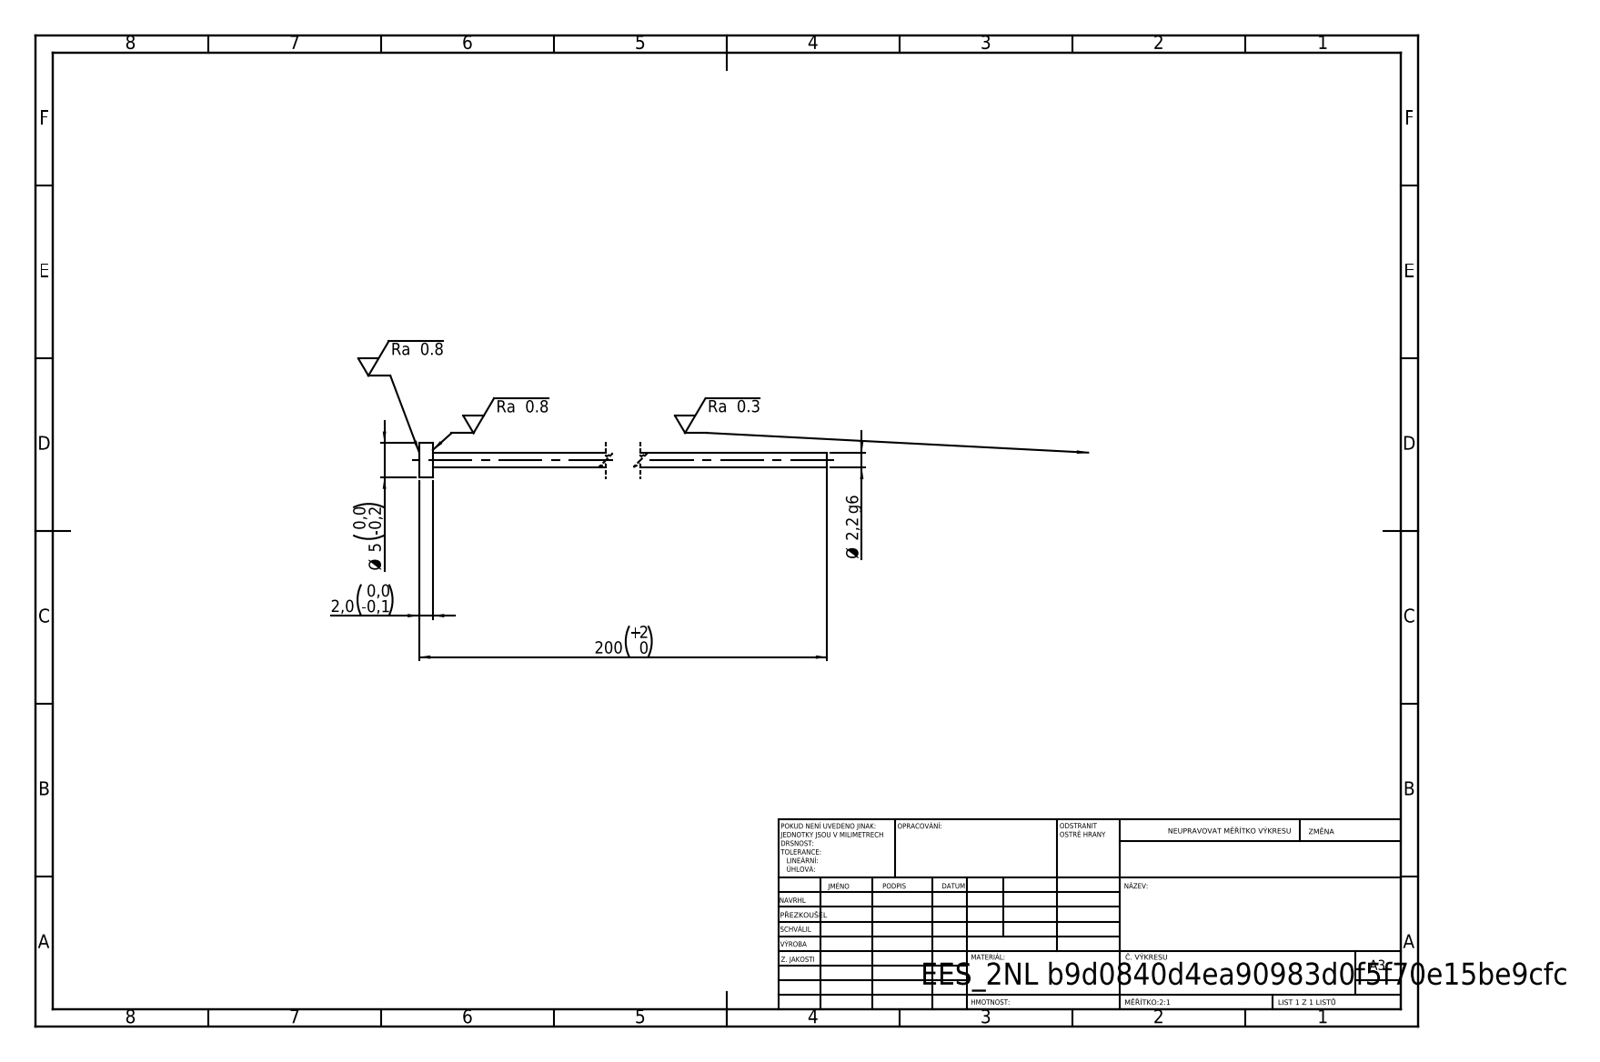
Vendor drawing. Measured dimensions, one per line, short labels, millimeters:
written by: SolidWorks 2019 (CONFIG_CONTROL_DESIGN)
unit: mm
bodies: 1 solid, 7 faces (3 planar, 4 cylindrical, 0 other)
size: 200 × 5 × 5
volume: 792 mm³; area: 1 439 mm²
bosses: 1× ⌀5, 1× ⌀2.2
face distances: 2, 200, 198
